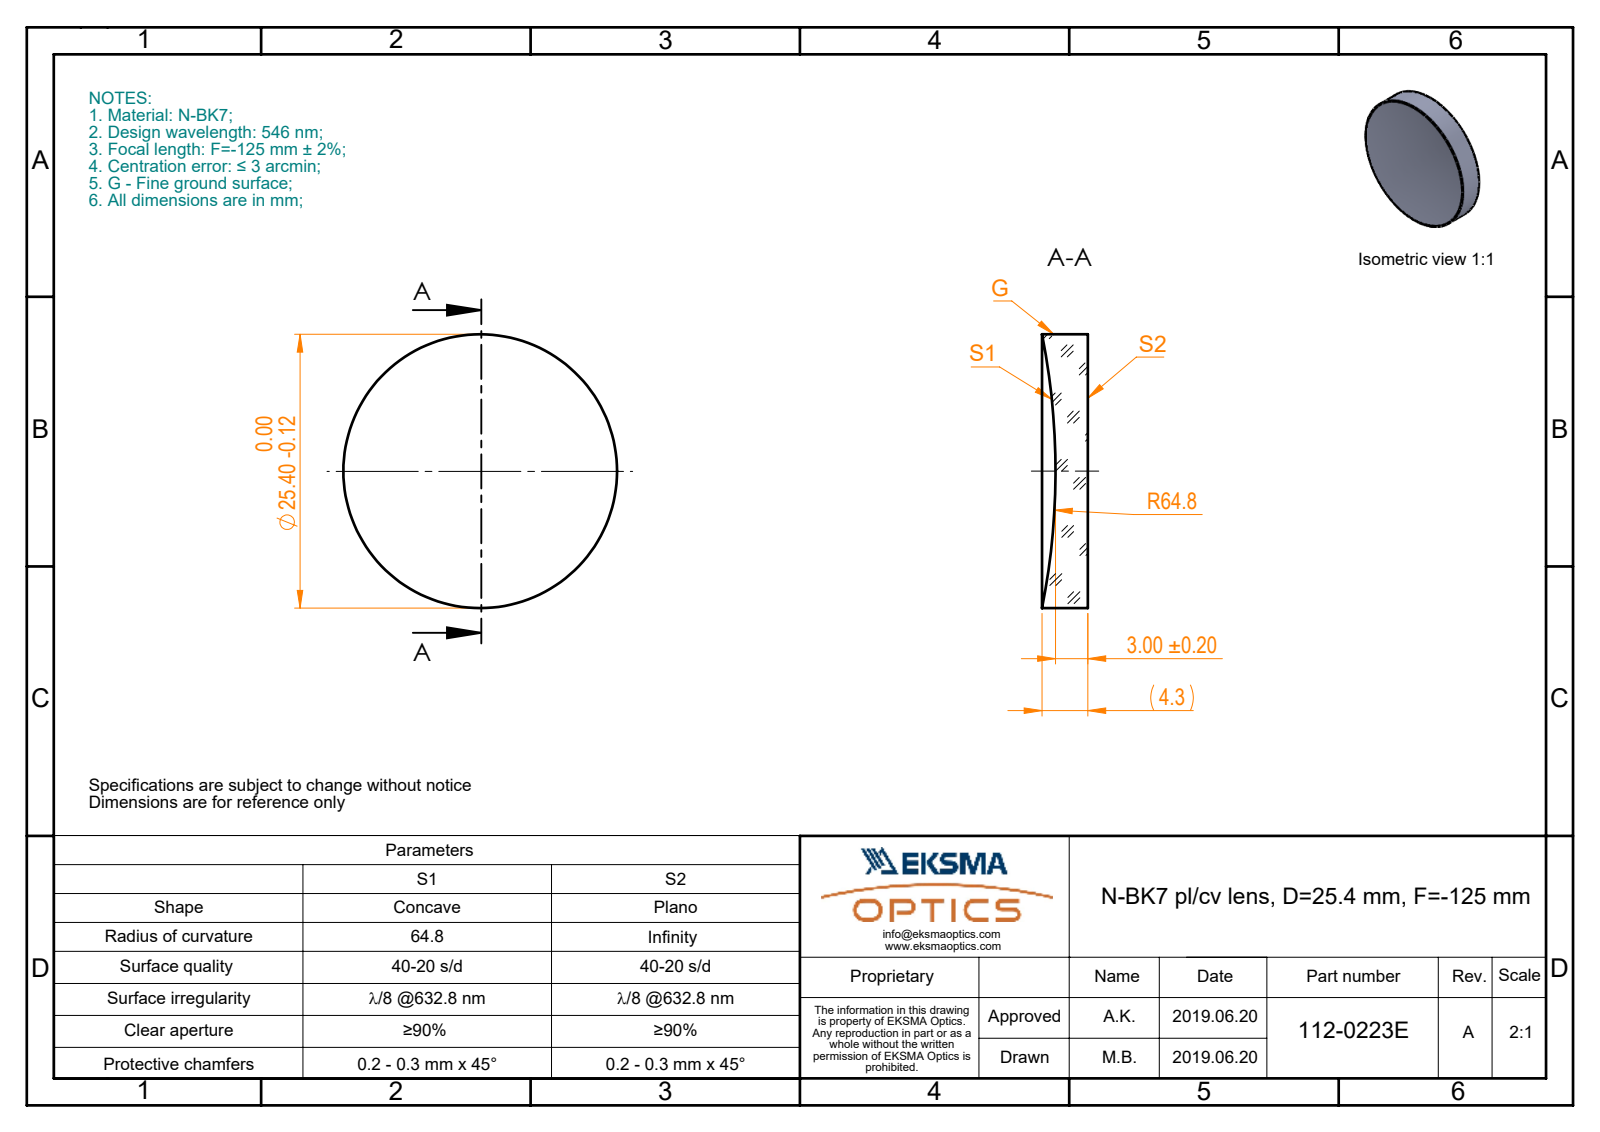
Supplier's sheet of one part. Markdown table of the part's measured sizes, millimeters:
| quantity | value |
| --- | --- |
| part name | 112-0223E BK7 pl-cv 25.4 F-125 |
| STEP written by | SolidWorks 2017 (CONFIG_CONTROL_DESIGN) |
| units | millimeters |
| bodies | 1 solid, 5 faces (1 planar, 2 cylindrical, 2 other) |
| overall size | 25.4 × 25.4 × 4.26 |
| volume | 1 837 mm³ |
| surface area | 1 358 mm² |
| round bosses / shafts (diameter × count) | 25.4 × 1 |
